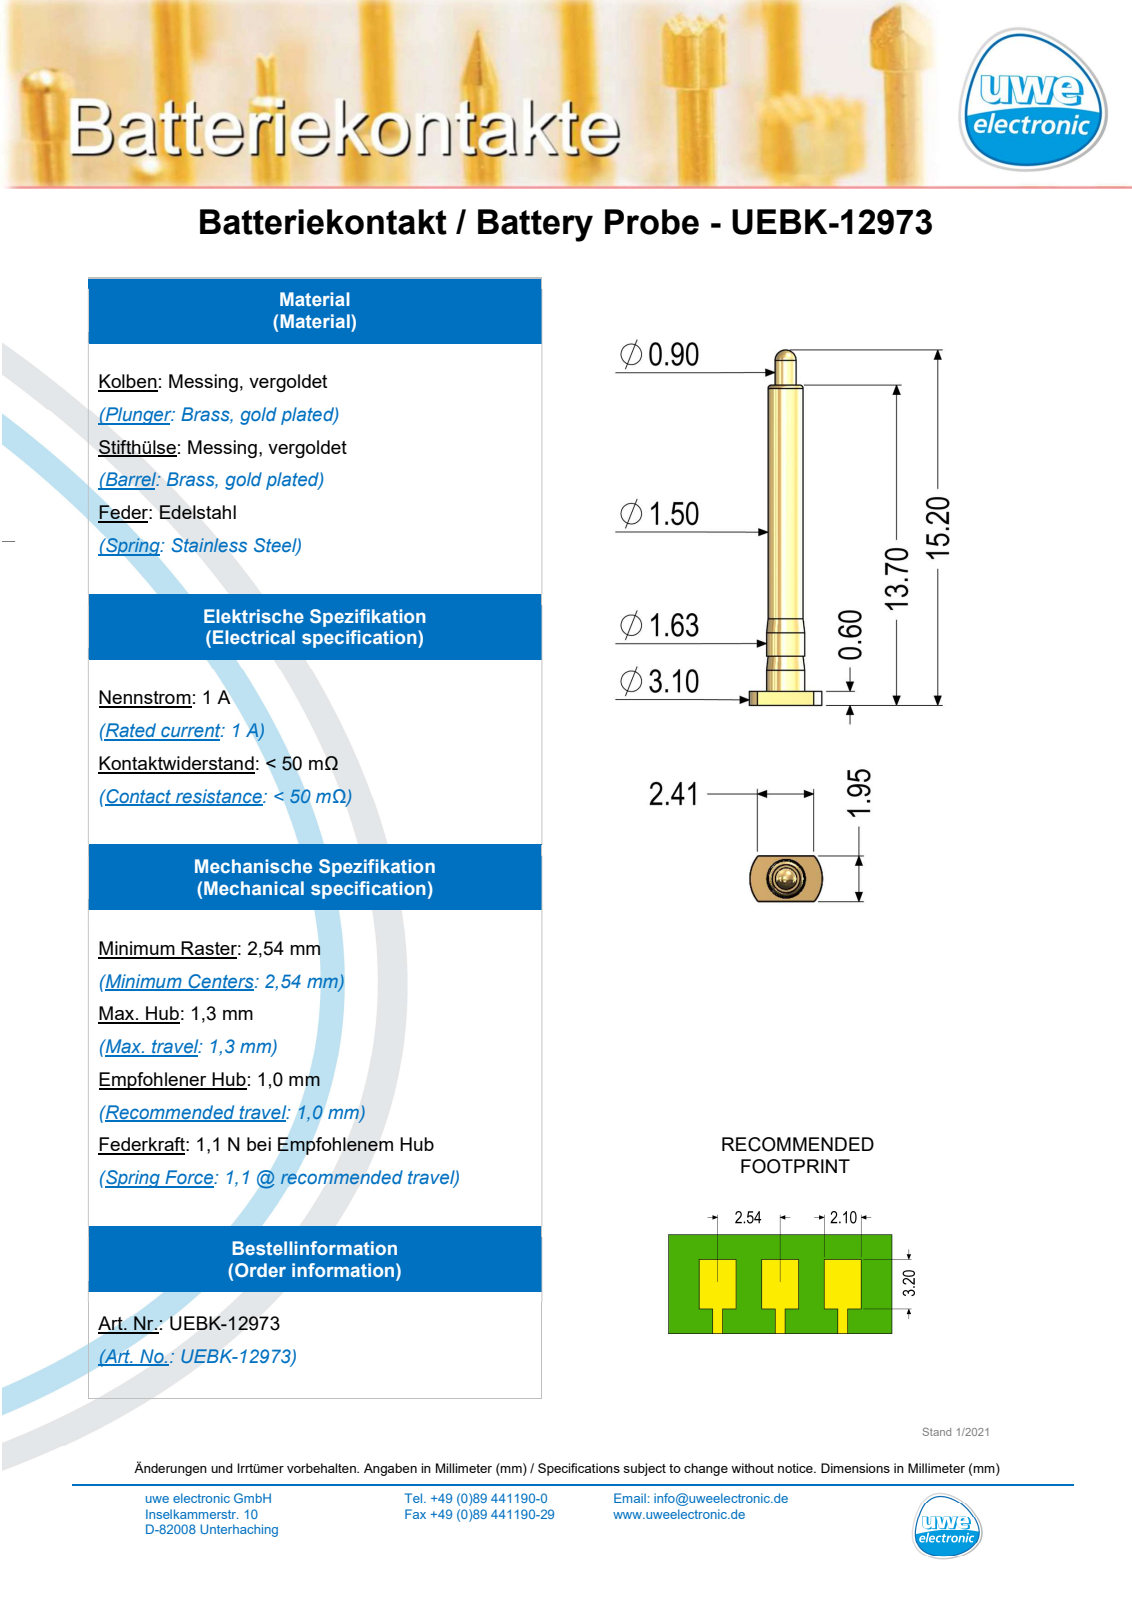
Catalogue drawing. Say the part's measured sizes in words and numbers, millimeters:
The part is named "UEBK-12973_2017_08_28". Its 3-D file was written by "SolidWorks 2017 (AUTOMOTIVE_DESIGN)". It is 1 solid with 25 faces: 6 planar, 11 cylindrical and 8 other. Overall it measures 15.22 by 3.1 by 1.95 millimeters. Its volume is 28 cubic millimeters and its surface area 83 square millimeters. Round bosses or shafts: 1 of diameter 1.63, 1 of diameter 1.5, 1 of diameter 0.9. Partial cylindrical surfaces (rounded edges, fillets, slot ends): 1 of radius 1.55. The main face-to-face distances are 0.6, 1.95, 13.1, 13.7, 11.6, 1.5, 2.1.
